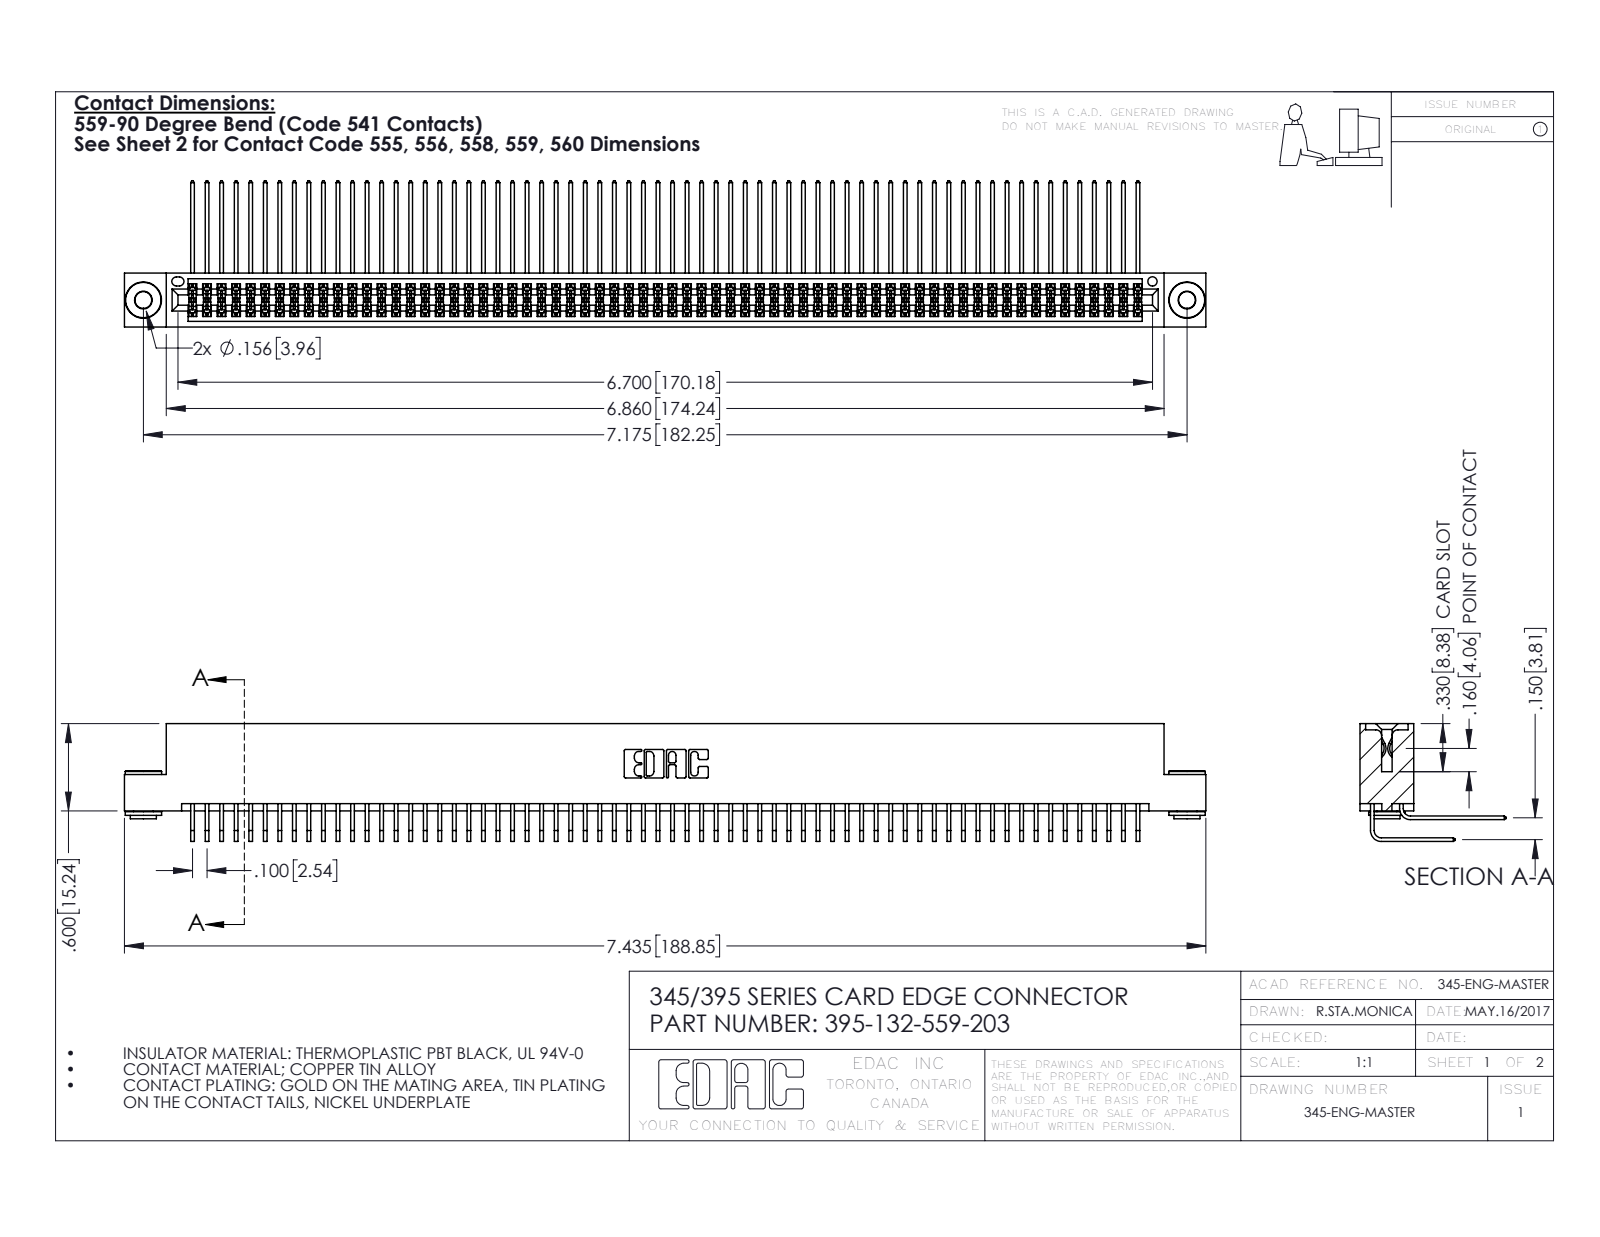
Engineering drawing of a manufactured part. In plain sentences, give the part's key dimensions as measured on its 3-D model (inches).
The part is named "395-132-559-203; 345-250-002_345-250-002-102; 345-292-001_558 559 Tail - 1; 345-292-001_559 Tail - 2 (+1 more)". Its 3-D file was written by "SolidWorks 2016 (CONFIG_CONTROL_DESIGN)". It is 135 solids with 7028 faces: 4710 planar, 2310 cylindrical and 8 other. Overall it measures 7.435 by 1.005 by 0.809 inches. Its volume is 1.181 cubic inches and its surface area 50.92 square inches. Round holes: 2 of diameter 0.116, 2 of diameter 0.156, 1 of diameter 0.064. Round bosses or shafts: 2 of diameter 0.25, 2 of diameter 0.18, 2 of diameter 0.136. Partial cylindrical surfaces (rounded edges, fillets, slot ends): 199 of radius 0.006, 22 of radius 0.01, 6 of radius 0.007, 6 of radius 0.031, 3 of radius 0.026, 2 of radius 0.014, 2 of radius 0.019, 2 of radius 0.022. The main face-to-face distances are 0.072, 0.298, 0.2, 0.37, 0.025, 0.098, 0.272, 0.225, 0.175, 0.15. The hole center spacings are 0.27, 6.939, 7.175.
